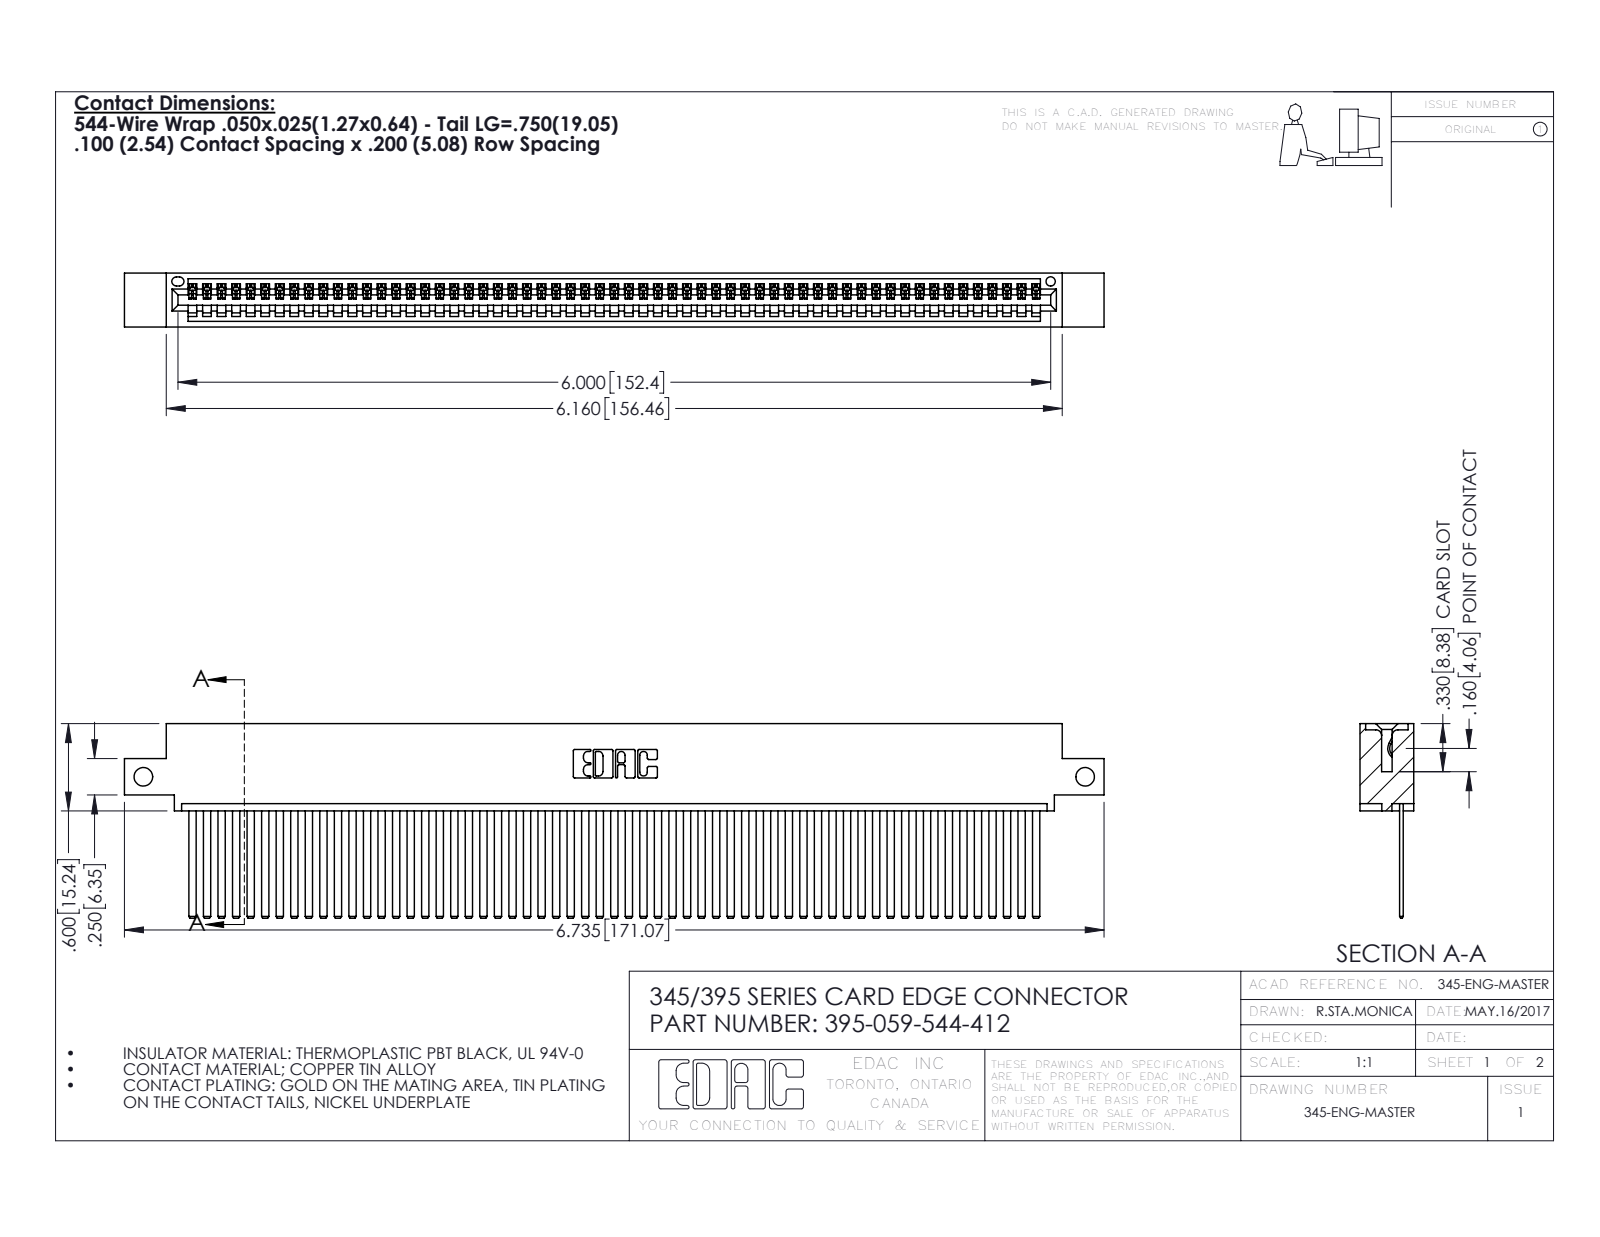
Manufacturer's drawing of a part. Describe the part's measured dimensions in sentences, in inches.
The part is named "345-292-001_345-293-144; 345 Part_0.110 Offset - Side Mount; 395-059-544-412". Its 3-D file was written by "SolidWorks 2016 (CONFIG_CONTROL_DESIGN)". It is 60 solids with 3198 faces: 2208 planar, 990 cylindrical and 0 other. Overall it measures 6.735 by 1.337 by 0.37 inches. Its volume is 1.032 cubic inches and its surface area 38.28 square inches. Round holes: 2 of diameter 0.128, 1 of diameter 0.064. Partial cylindrical surfaces (rounded edges, fillets, slot ends): 118 of radius 0.006, 22 of radius 0.01, 6 of radius 0.007, 6 of radius 0.031, 3 of radius 0.026, 2 of radius 0.031, 2 of radius 0.04, 1 of radius 0.014. The main face-to-face distances are 0.072, 0.298, 0.025, 0.098, 0.272, 0.37, 0.2, 0.225, 0.149, 0.072. The hole center spacings are 6.475.
